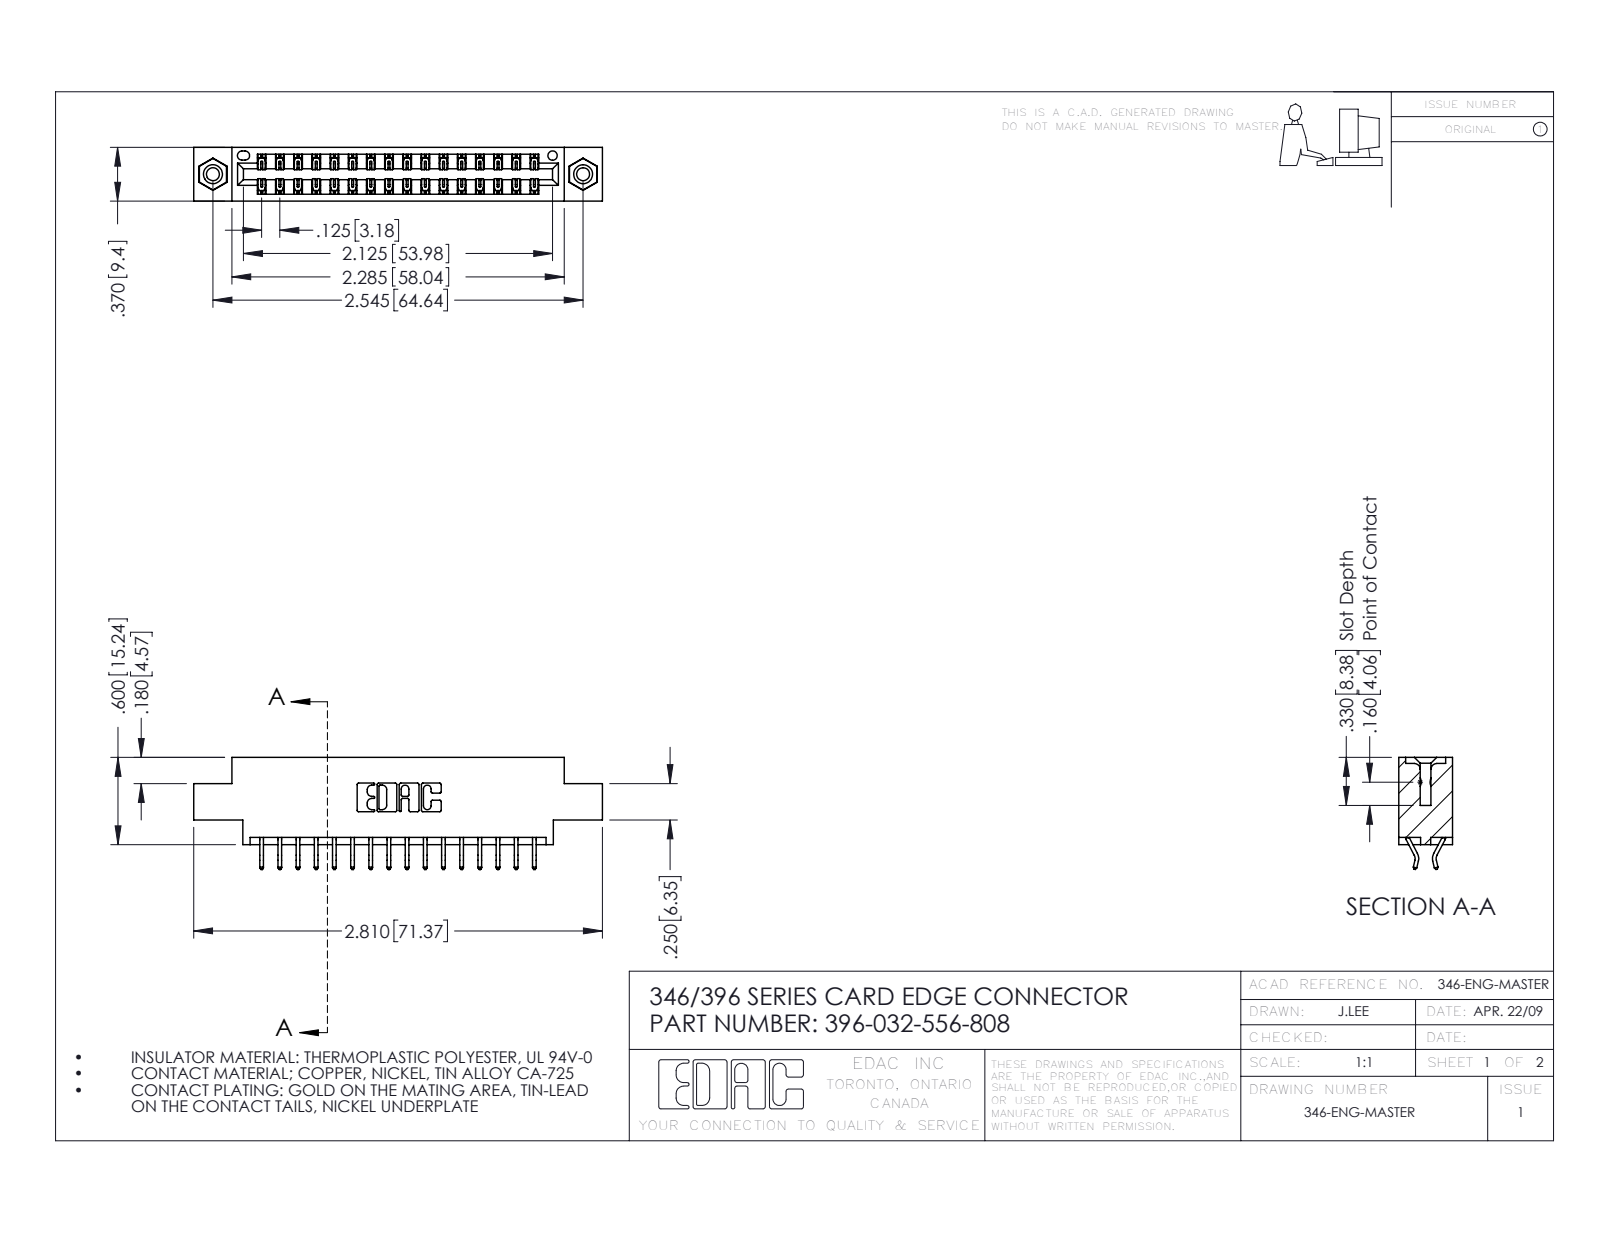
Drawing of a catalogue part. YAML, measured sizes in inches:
part_name: "345-292-001_556 Tail; 345-250-001_345-250-003-102; 346 Part_0.170 Offset - 0.156 Dia-TI; 396-032-556-808"
step_written_by: "SolidWorks 2016 (CONFIG_CONTROL_DESIGN)"
units: inches
bodies: {solids: 35, faces: 2042, planar: 1360, cylindrical: 666, other: 16}
overall_size: [2.81, 0.77, 0.37]
volume: 0.402
surface_area: 13.68
round_holes:
  - {diameter: 0.089, count: 2}
  - {diameter: 0.125, count: 2}
  - {diameter: 0.156, count: 2}
  - {diameter: 0.064, count: 1}
round_bosses_or_shafts:
  - {diameter: 0.155, count: 2}
partial_cylinders:
  - {radius: 0.006, count: 48}
  - {radius: 0.01, count: 22}
  - {radius: 0.007, count: 6}
  - {radius: 0.031, count: 6}
  - {radius: 0.026, count: 3}
  - {radius: 0.01, count: 2}
  - {radius: 0.014, count: 2}
  - {radius: 0.022, count: 2}
face_to_face_distances: [0.048, 0.322, 0.37, 0.25, 0.025, 0.072, 0.298, 0.222, 0.275, 0.148]
hole_center_spacings: [0.246, 2.338, 2.545]
